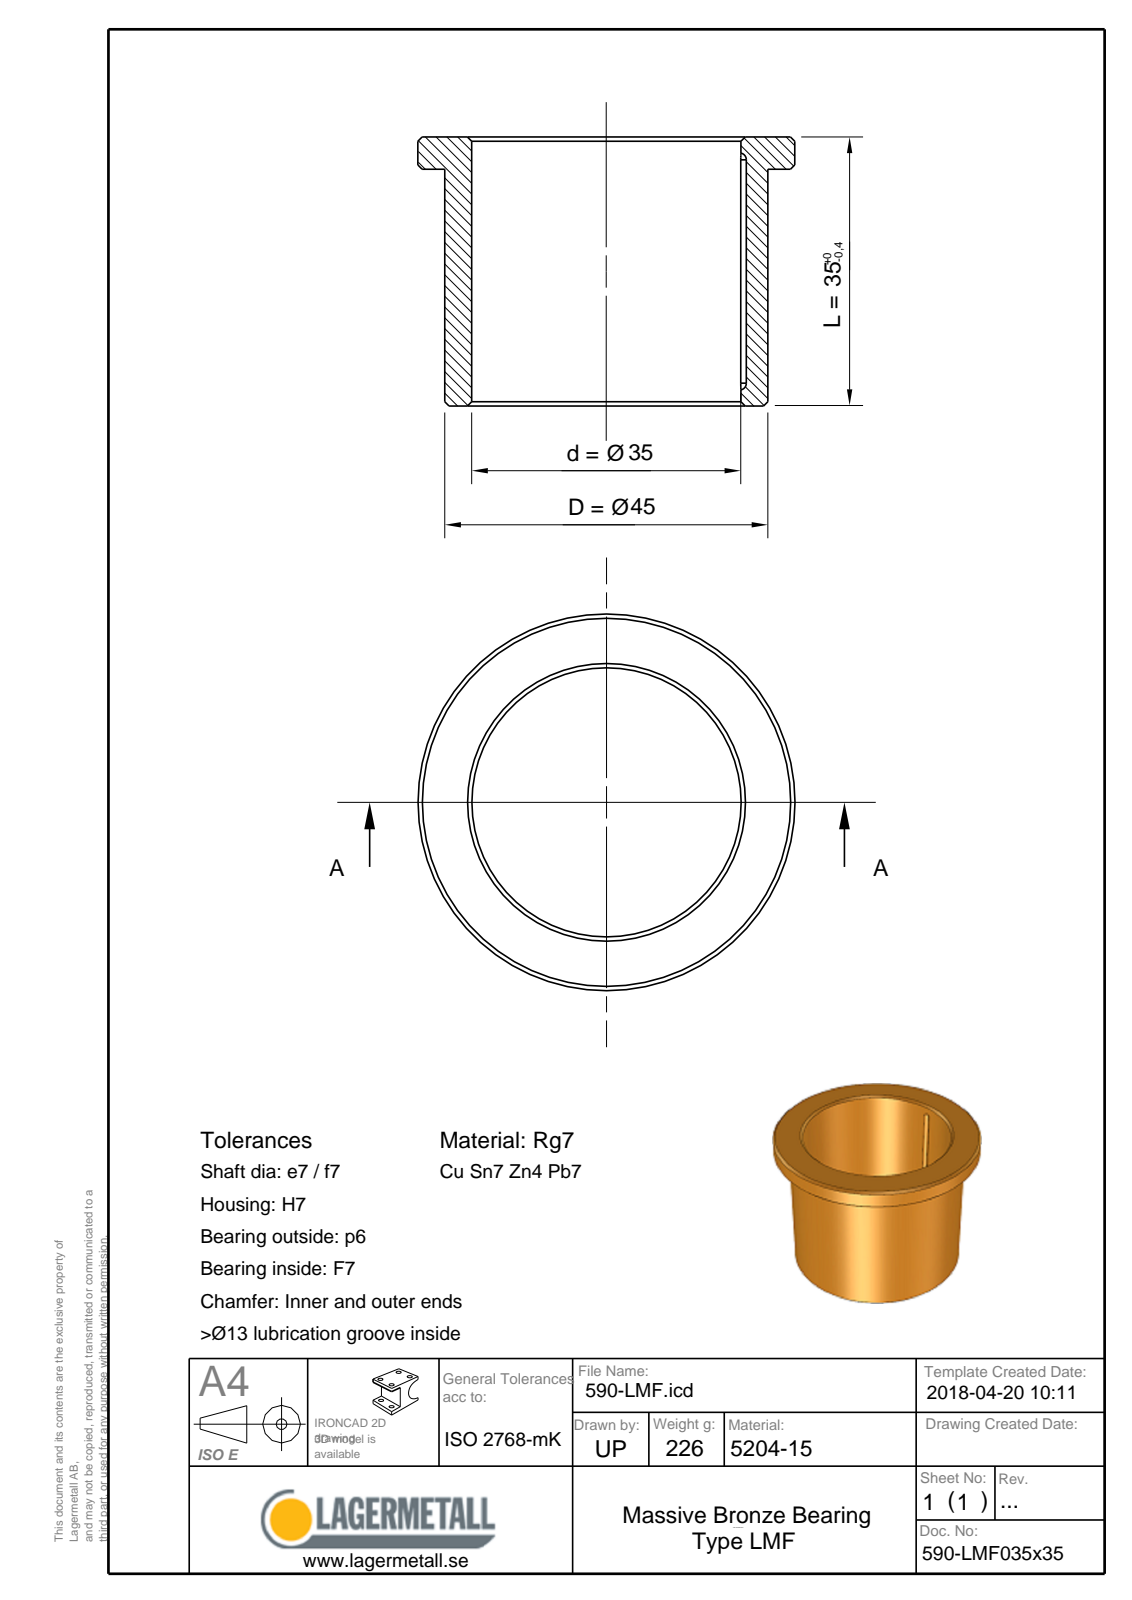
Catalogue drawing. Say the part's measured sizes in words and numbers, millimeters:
The part is named "590-LMF035x35". Its 3-D file was written by "Spatial InterOp 3D (CONFIG_CONTROL_DESIGN)". It is 1 solid with 16 faces: 4 planar, 5 cylindrical and 7 other. Overall it measures 55 by 55 by 35 millimeters. Its volume is 25 639 cubic millimeters and its surface area 11 480 square millimeters. Round holes: 1 of diameter 35. Round bosses or shafts: 1 of diameter 55, 1 of diameter 45. Partial cylindrical surfaces (rounded edges, fillets, slot ends): 2 of radius 1.25. The main face-to-face distances are 5, 30, 35.
